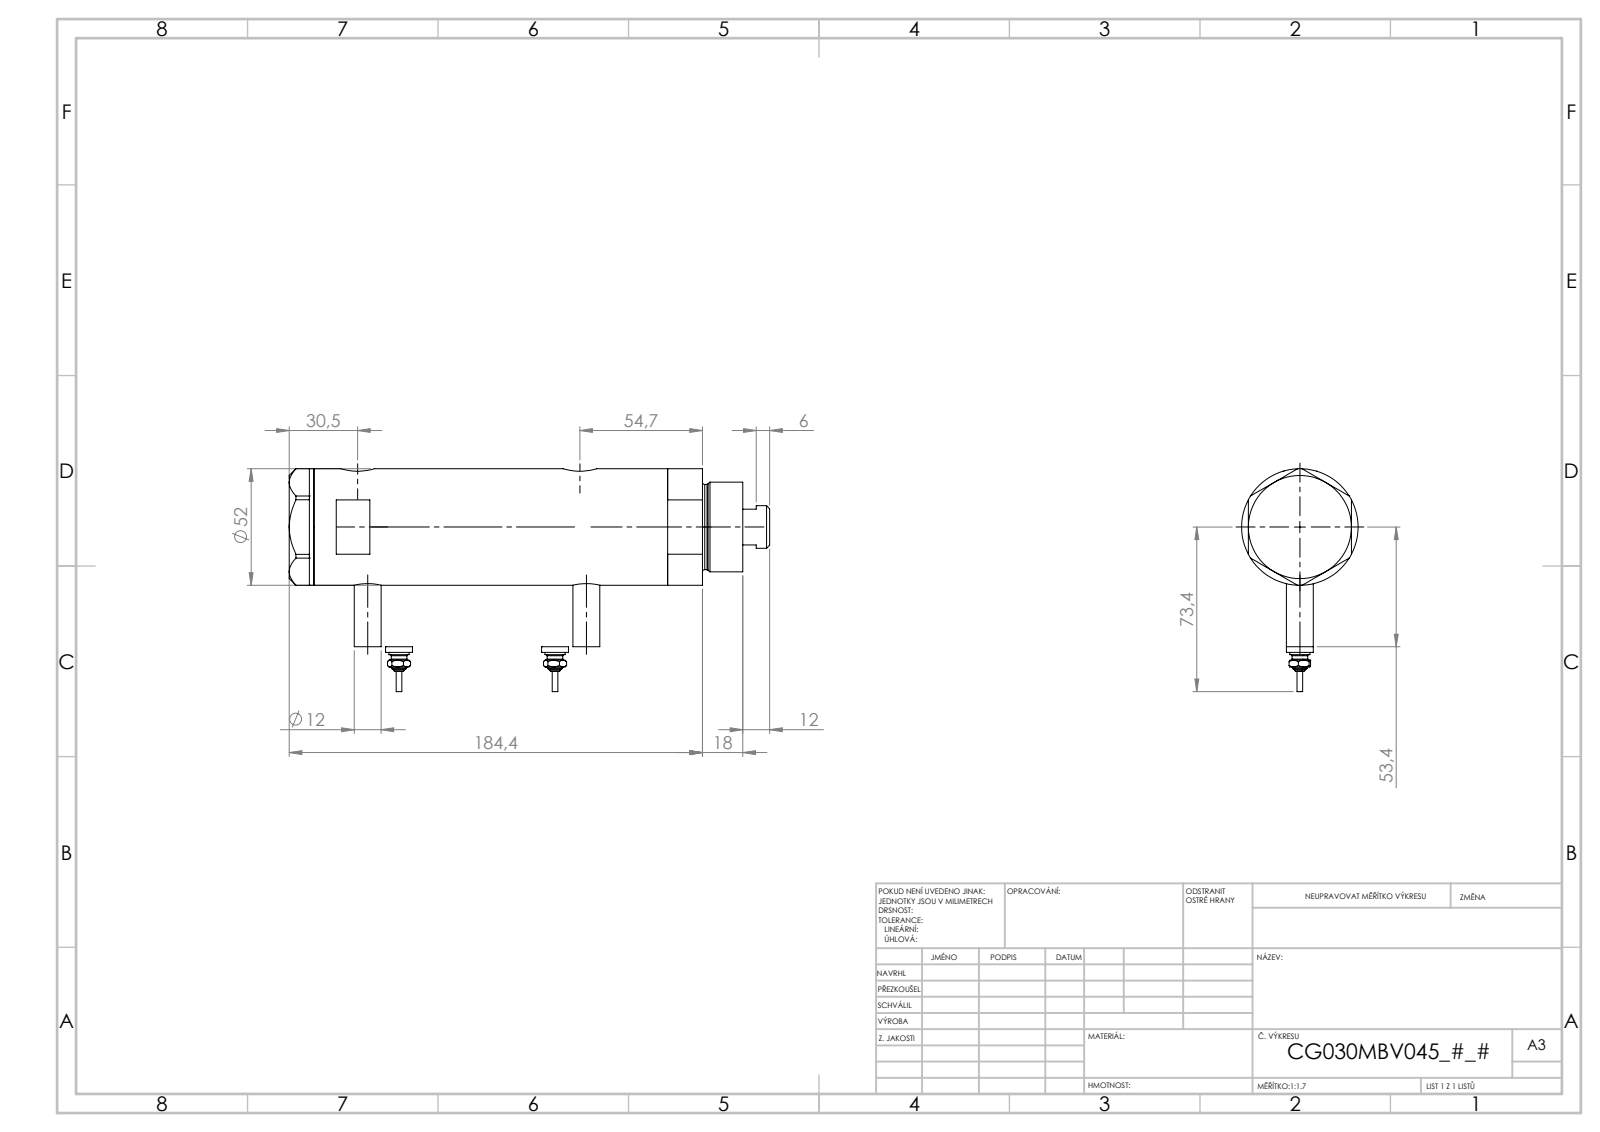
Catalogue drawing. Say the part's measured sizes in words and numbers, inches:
The part is named "V270CG_FRONT; V270CG_SWITCH; V270CG_MIDDLE; V270CG_VC (+1 more)". Its 3-D file was written by "SolidWorks 2019 (CONFIG_CONTROL_DESIGN)". It is 6 solids with 246 faces: 95 planar, 77 cylindrical and 74 other. Overall it measures 7.639 by 3.319 by 2.047 inches. Its volume is 21.25 cubic inches and its surface area 126.3 square inches. Round holes: 2 of diameter 0.197, 2 of diameter 0.383, 2 of diameter 0.492, 2 of diameter 0.591, 1 of diameter 0.256, 1 of diameter 0.787, 1 of diameter 0.846, 1 of diameter 1.181, 1 of diameter 1.299, 1 of diameter 1.732. Round bosses or shafts: 3 of diameter 0.472, 2 of diameter 0.354, 2 of diameter 0.276, 2 of diameter 0.171, 2 of diameter 0.094, 1 of diameter 2.047, 1 of diameter 1.575, 1 of diameter 1.496. The main face-to-face distances are 3.88, 0.937, 2.943, 0.433, 1.37, 4.313, 1.811, 5.746, 5.313, 4.376. The hole center spacings are 0.114, 0.177, 2.825, 2.939, 3.002, 3.116, 0.114, 0.115.
